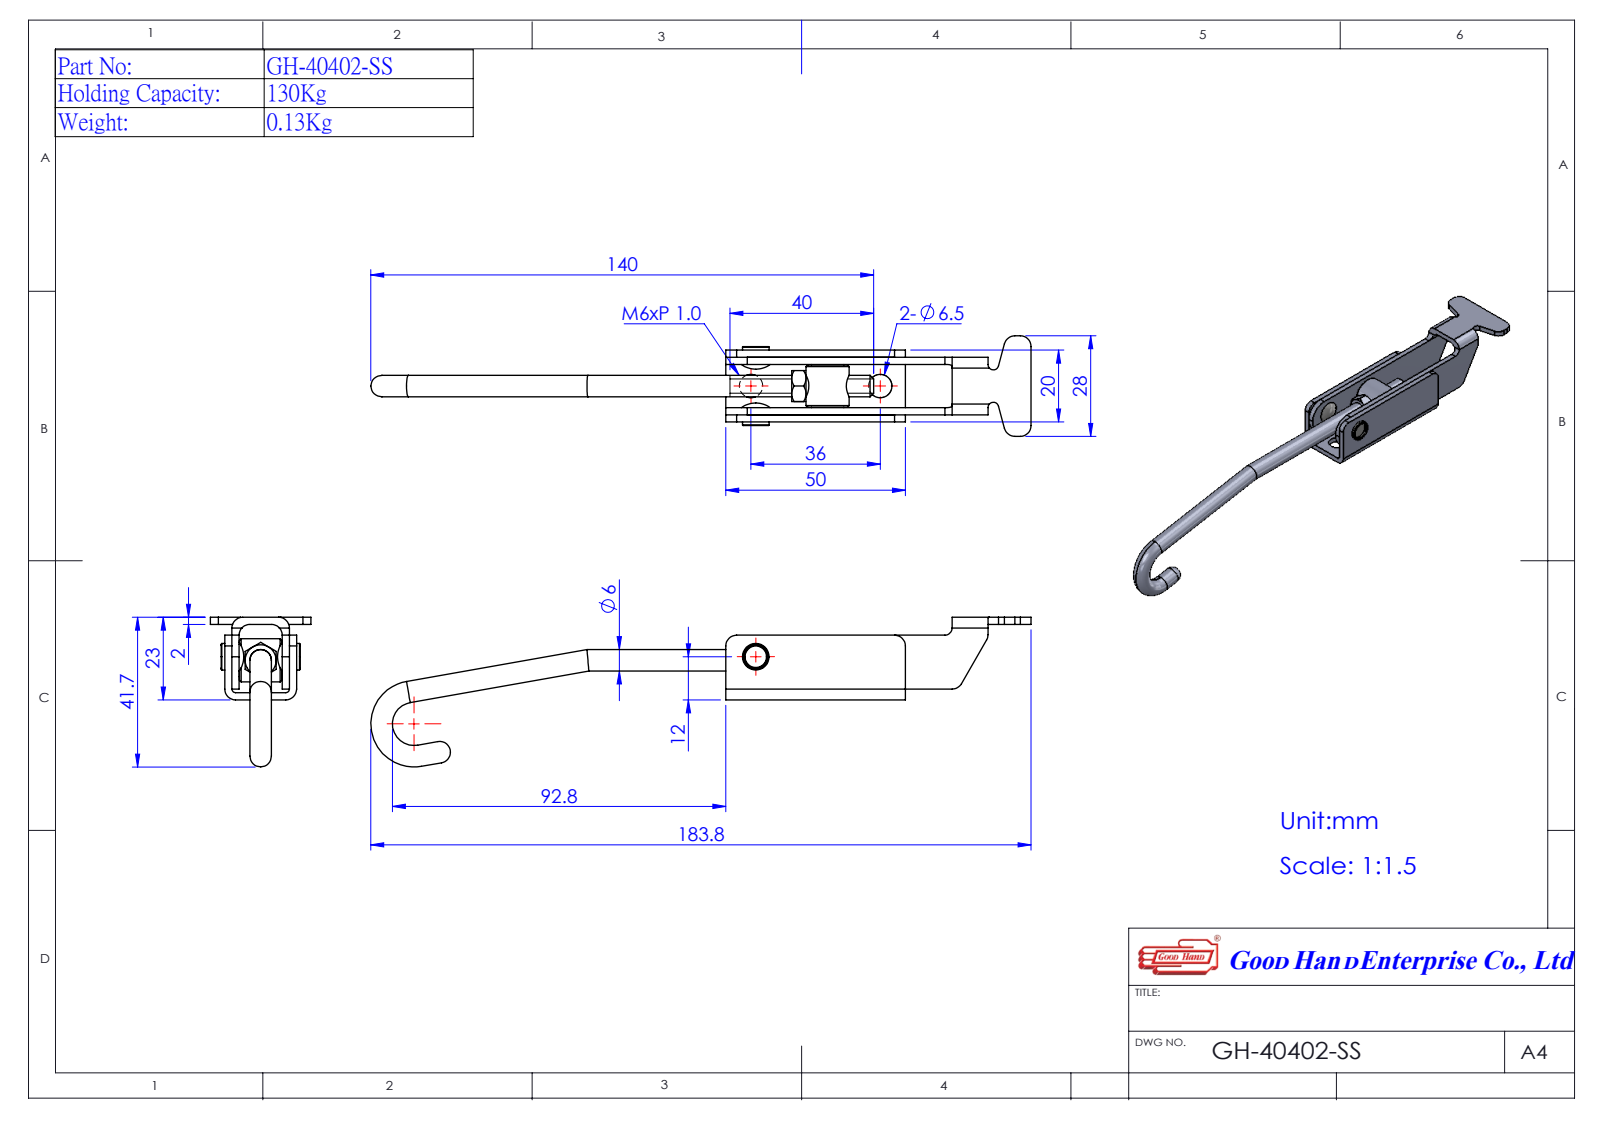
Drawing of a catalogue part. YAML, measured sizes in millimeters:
part_name: "14040213-1^GH-40402(簡化); GH-40402-SS(簡化); Group3^GH-40402(簡化); Group1^GH-40402(簡化) (+1 more)"
step_written_by: "SolidWorks 2016 (AUTOMOTIVE_DESIGN)"
units: millimeters
bodies: {solids: 5, faces: 127, planar: 48, cylindrical: 58, other: 21}
overall_size: [183.84, 41.68, 28]
volume: 16018
surface_area: 15744
round_holes:
  - {diameter: 6.5, count: 2}
  - {diameter: 5, count: 1}
  - {diameter: 6, count: 1}
  - {diameter: 8, count: 1}
round_bosses_or_shafts:
  - {diameter: 6, count: 2}
  - {diameter: 12, count: 1}
  - {diameter: 7.4, count: 1}
partial_cylinders:
  - {radius: 3, count: 8}
  - {radius: 1.5, count: 2}
  - {radius: 2, count: 1}
  - {radius: 6, count: 1}
  - {radius: 9, count: 1}
face_to_face_distances: [2, 16, 18, 14, 4, 20, 12, 21, 3, 5]
hole_center_spacings: [20.02, 36]
